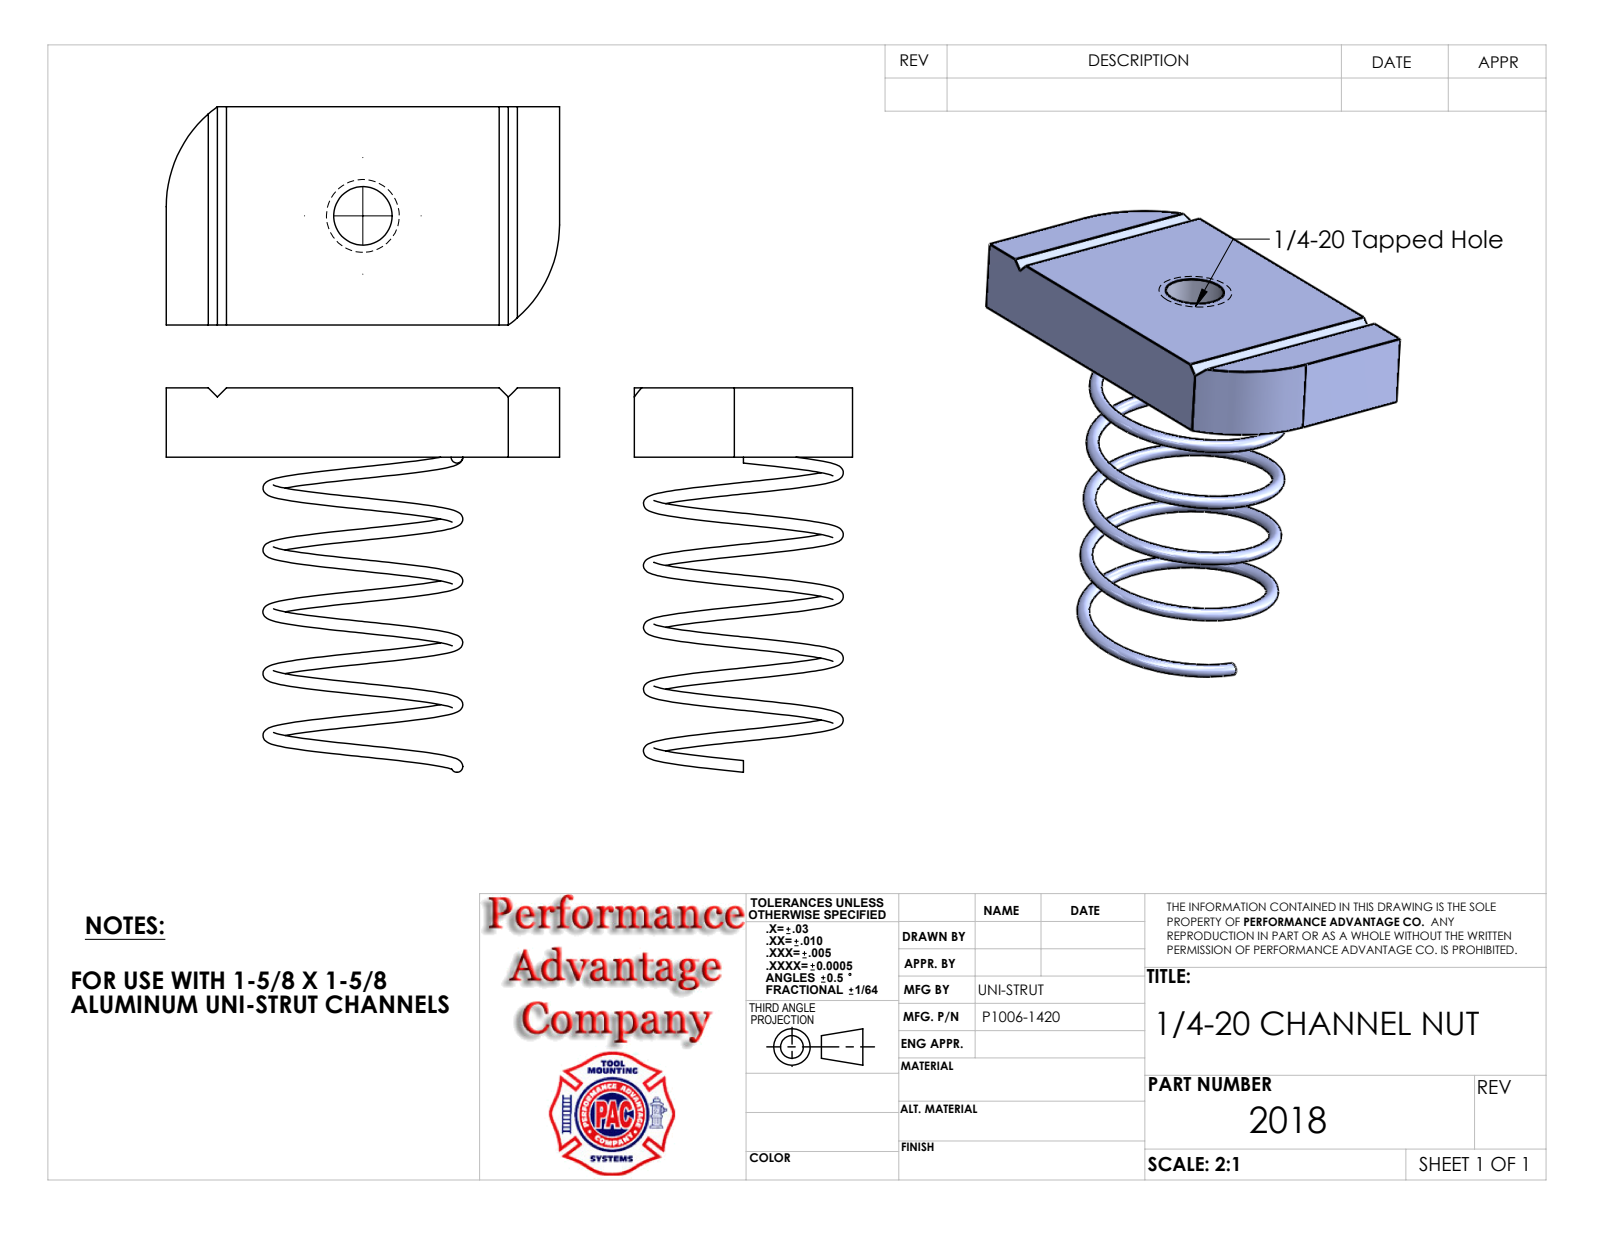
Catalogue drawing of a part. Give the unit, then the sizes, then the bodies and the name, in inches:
Units: inches
Overall size (bounding box): 1.352 × 1.321 × 0.75
Round holes (diameter × count): ⌀0.201 ×1
Partial cylindrical surfaces — rounded edges, fillets, slot ends (radius × count): R0.424 ×2
Main face-to-face distances: 0.238, 0.75, 1.352, 0.707, 0.375
Volume: 0.236 in³ · Surface area: 4.289 in²
Bodies: 1 solid, 20 faces (14 planar, 4 cylindrical, 2 other)
Part name (STEP PRODUCT): 2018
STEP written by: SolidWorks 2010 (CONFIG_CONTROL_DESIGN)
